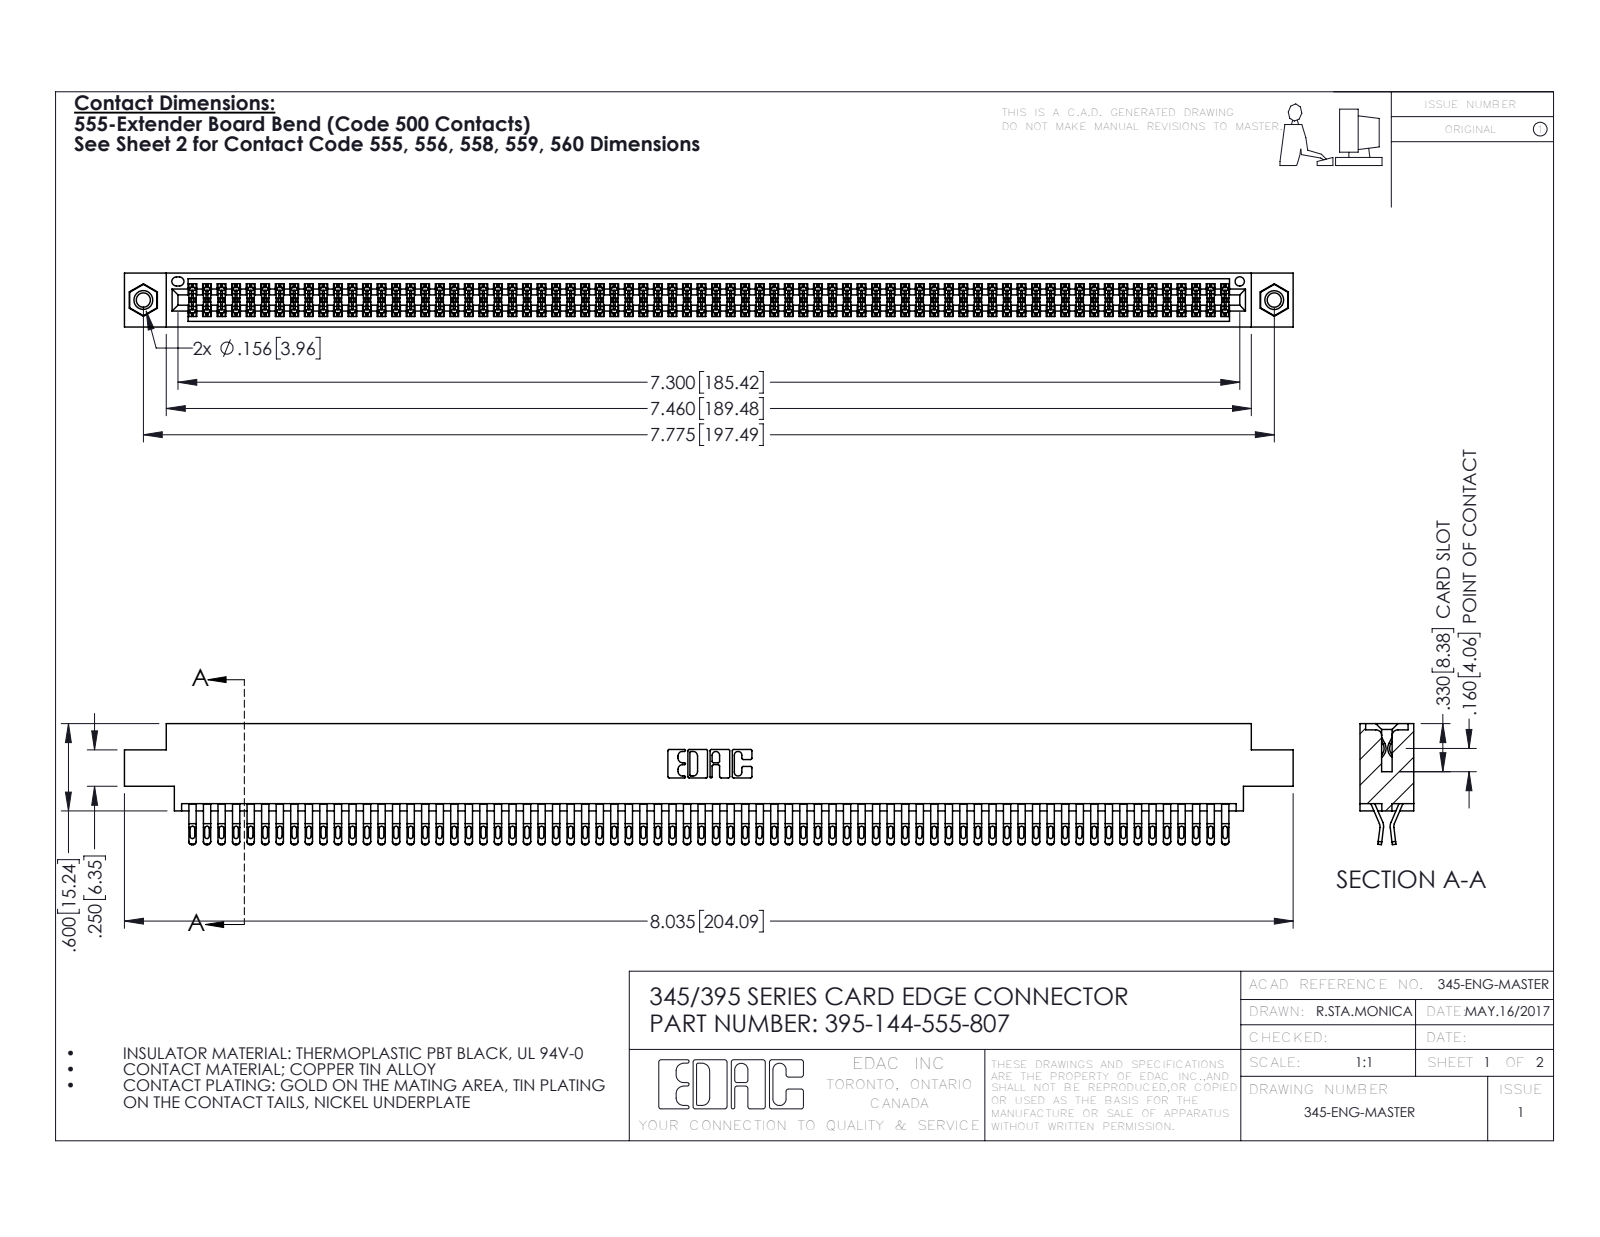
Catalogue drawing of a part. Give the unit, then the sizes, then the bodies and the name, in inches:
Units: inches
Overall size (bounding box): 8.035 × 0.832 × 0.37
Round holes (diameter × count): ⌀0.098 ×2, ⌀0.125 ×2, ⌀0.156 ×2, ⌀0.064 ×1
Round bosses / shafts (diameter × count): ⌀0.155 ×2
Partial cylindrical surfaces — rounded edges, fillets, slot ends (radius × count): R0.016 ×360, R0.02 ×288, R0.006 ×216, R0.01 ×22, R0.007 ×6, R0.031 ×6, R0.026 ×3, R0.01 ×2
Main face-to-face distances: 0.072, 0.298, 0.025, 0.37, 0.2, 0.098, 0.272, 0.225, 0.175, 0.149
Hole centre spacings: 0.27, 7.539, 7.775
Volume: 1.245 in³ · Surface area: 50.15 in²
Bodies: 147 solids, 8254 faces (4580 planar, 3658 cylindrical, 16 other)
Part name (STEP PRODUCT): 345-292-001_555 Tail; 395-144-555-807; 345 Part_0.170 Offset - 0.156 Dia-TI; 345-250-001_345-250-005-103
STEP written by: SolidWorks 2016 (CONFIG_CONTROL_DESIGN)
